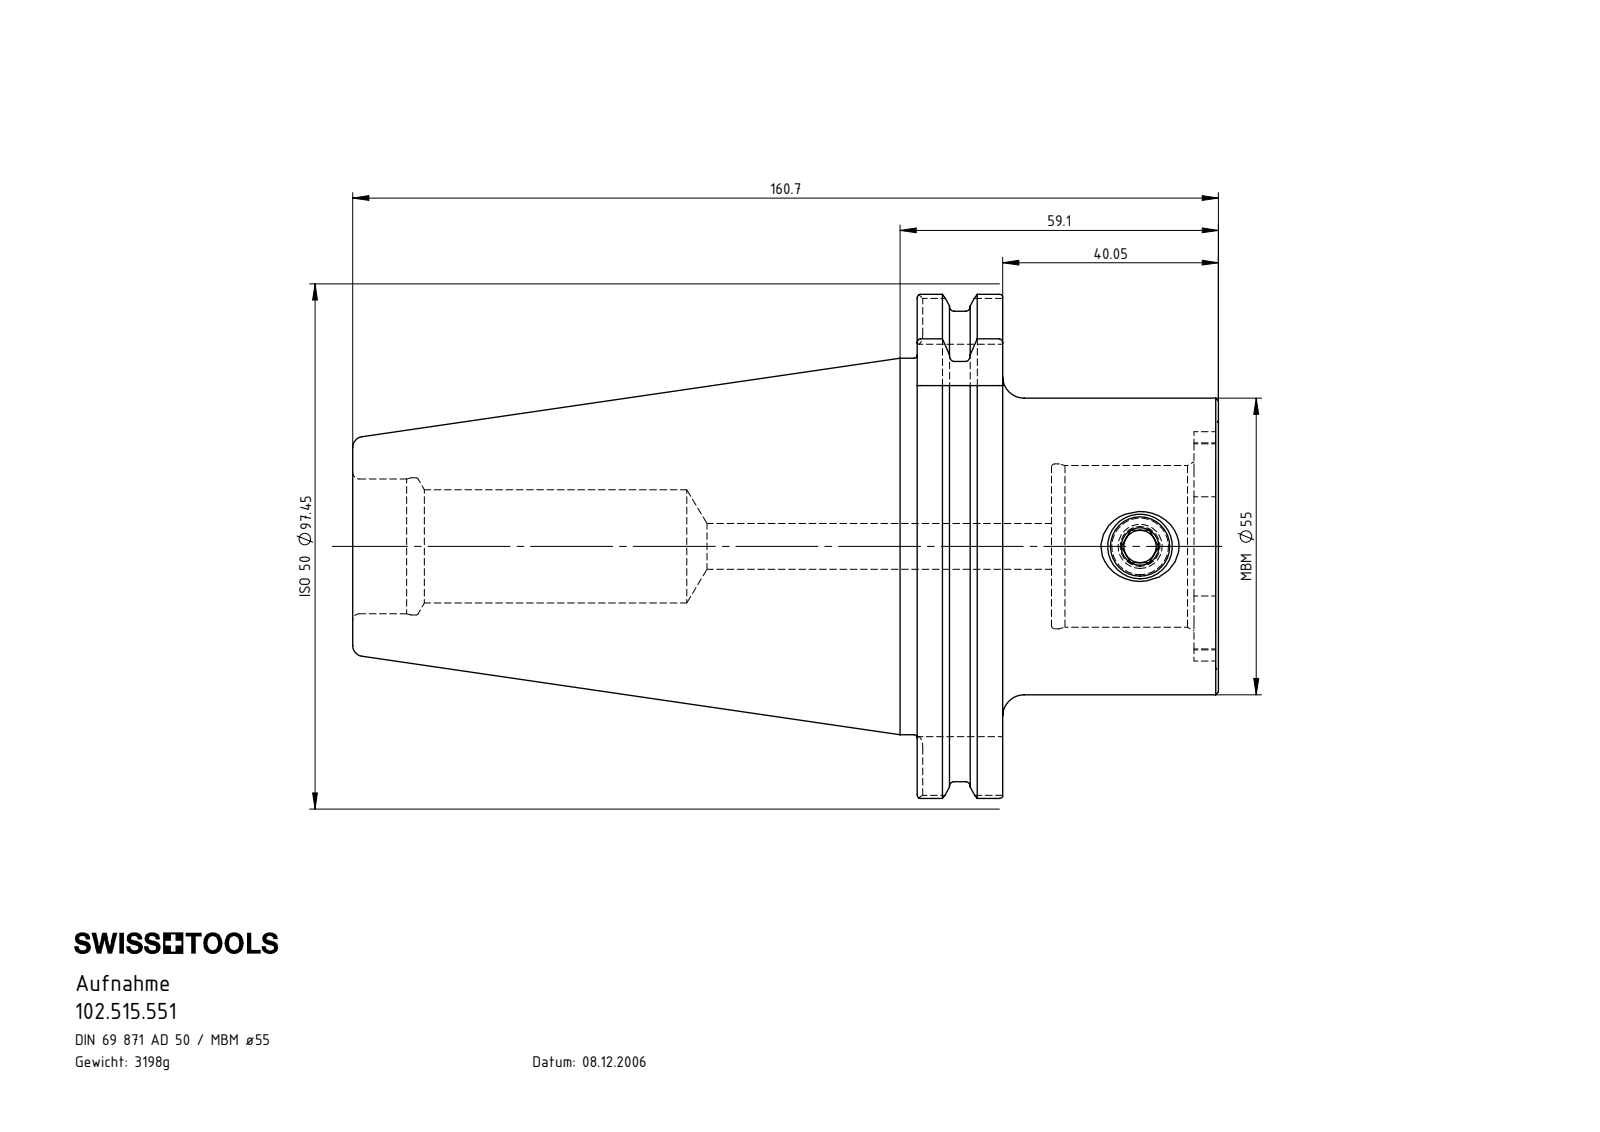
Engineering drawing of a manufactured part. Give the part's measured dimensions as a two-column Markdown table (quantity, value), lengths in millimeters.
| quantity | value |
| --- | --- |
| part name | MB5-ER1.001.017_A; 102.515.551; SK5-MB5.K01.059_C |
| STEP written by | SolidWorks 2017 (CONFIG_CONTROL_DESIGN) |
| units | millimeters |
| bodies | 2 solids, 169 faces (55 planar, 50 cylindrical, 64 other) |
| overall size | 160.7 × 97.45 × 93.51 |
| volume | 407 402 mm³ |
| surface area | 52 020 mm² |
| round holes (diameter × count) | 6 × 1, 8.5 × 1, 11 × 1, 21 × 1, 25 × 1, 25.45 × 1, 30 × 1, 30.6 × 1 |
| round bosses / shafts (diameter × count) | 91 × 1, 69.85 × 1, 55 × 1, 12 × 1 |
| partial cylindrical surfaces (radius × count) | 2 × 8, 5.2 × 4, 18.5 × 1, 21.27 × 1, 48.73 × 1 |
| main face-to-face distances | 15.85, 24.9, 9.05, 55.9, 40.05, 31, 51.35, 35.5, 26.45, 4.55 |
